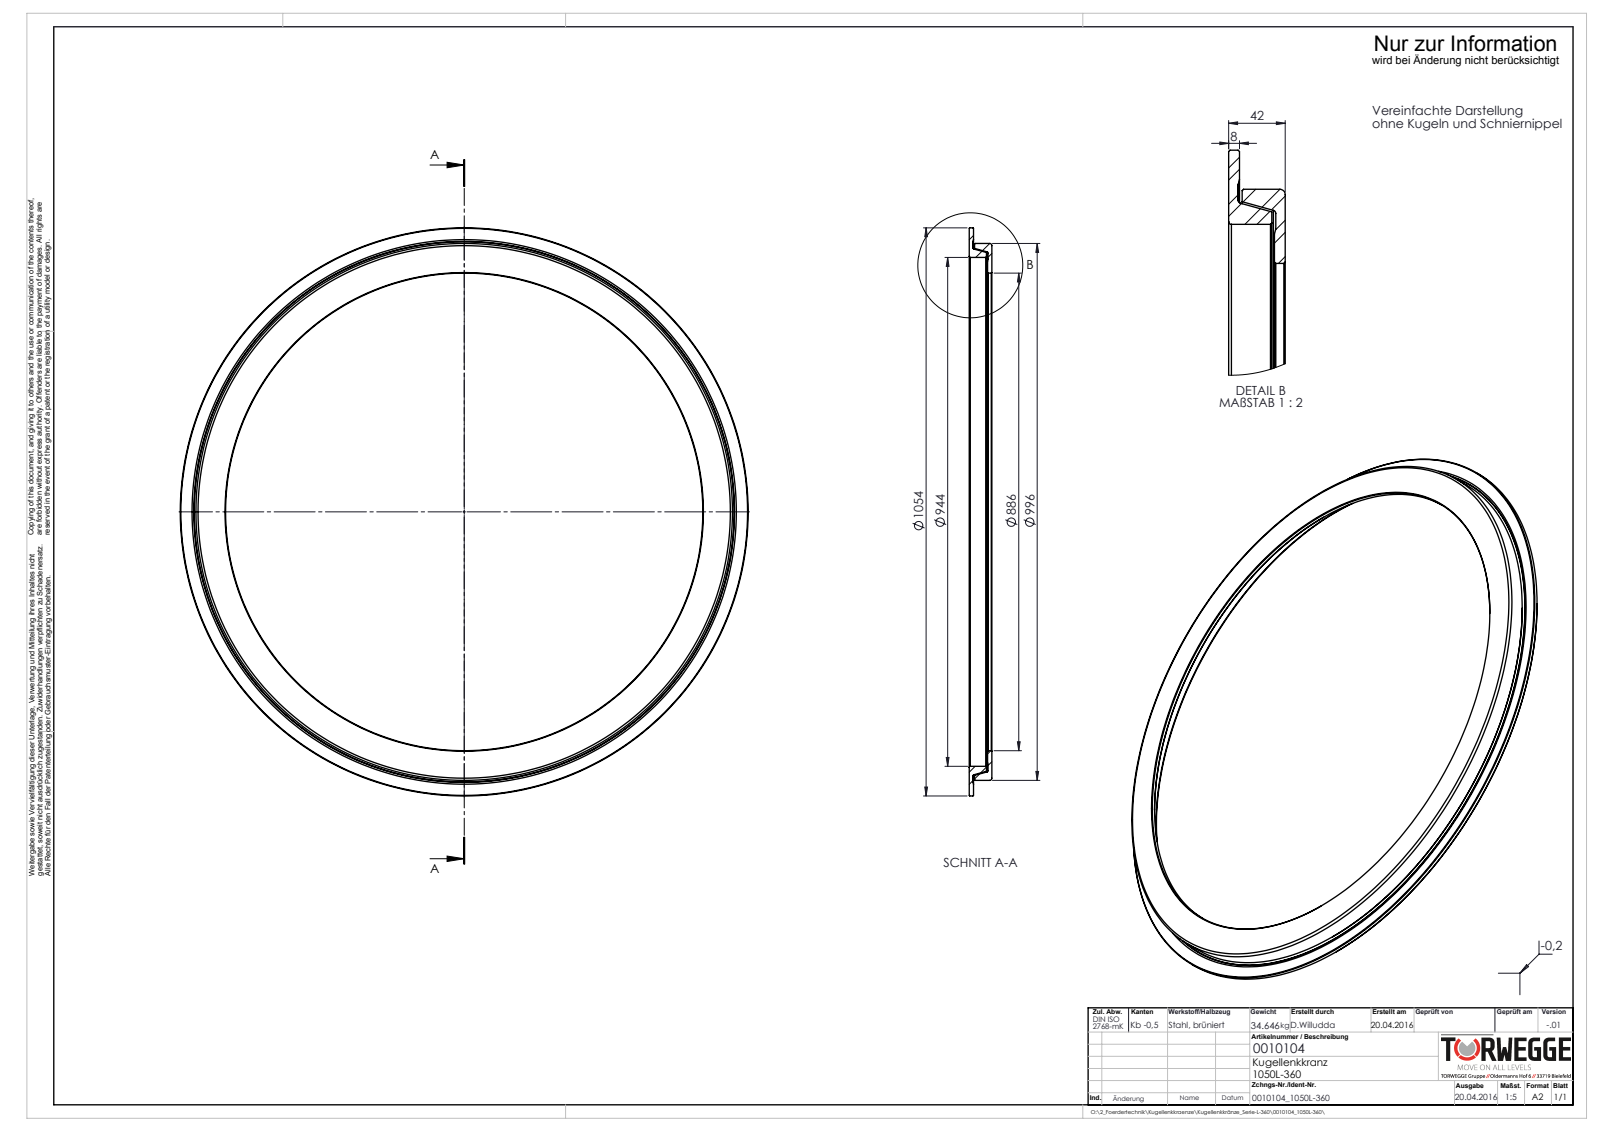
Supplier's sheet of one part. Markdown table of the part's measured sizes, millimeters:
| quantity | value |
| --- | --- |
| part name | 0010104_1050L-360 |
| STEP written by | SolidWorks 2016 (AUTOMOTIVE_DESIGN) |
| units | millimeters |
| bodies | 2 solids, 48 faces (8 planar, 8 cylindrical, 32 other) |
| overall size | 1054 × 1054 × 42 |
| volume | 4 402 000 mm³ |
| surface area | 1 009 000 mm² |
| round holes (diameter × count) | 886 × 1, 944 × 1 |
| round bosses / shafts (diameter × count) | 1054 × 1, 996 × 1 |
| main face-to-face distances | 42, 8, 34, 7, 35, 1, 27, 26, 10, 32 |
